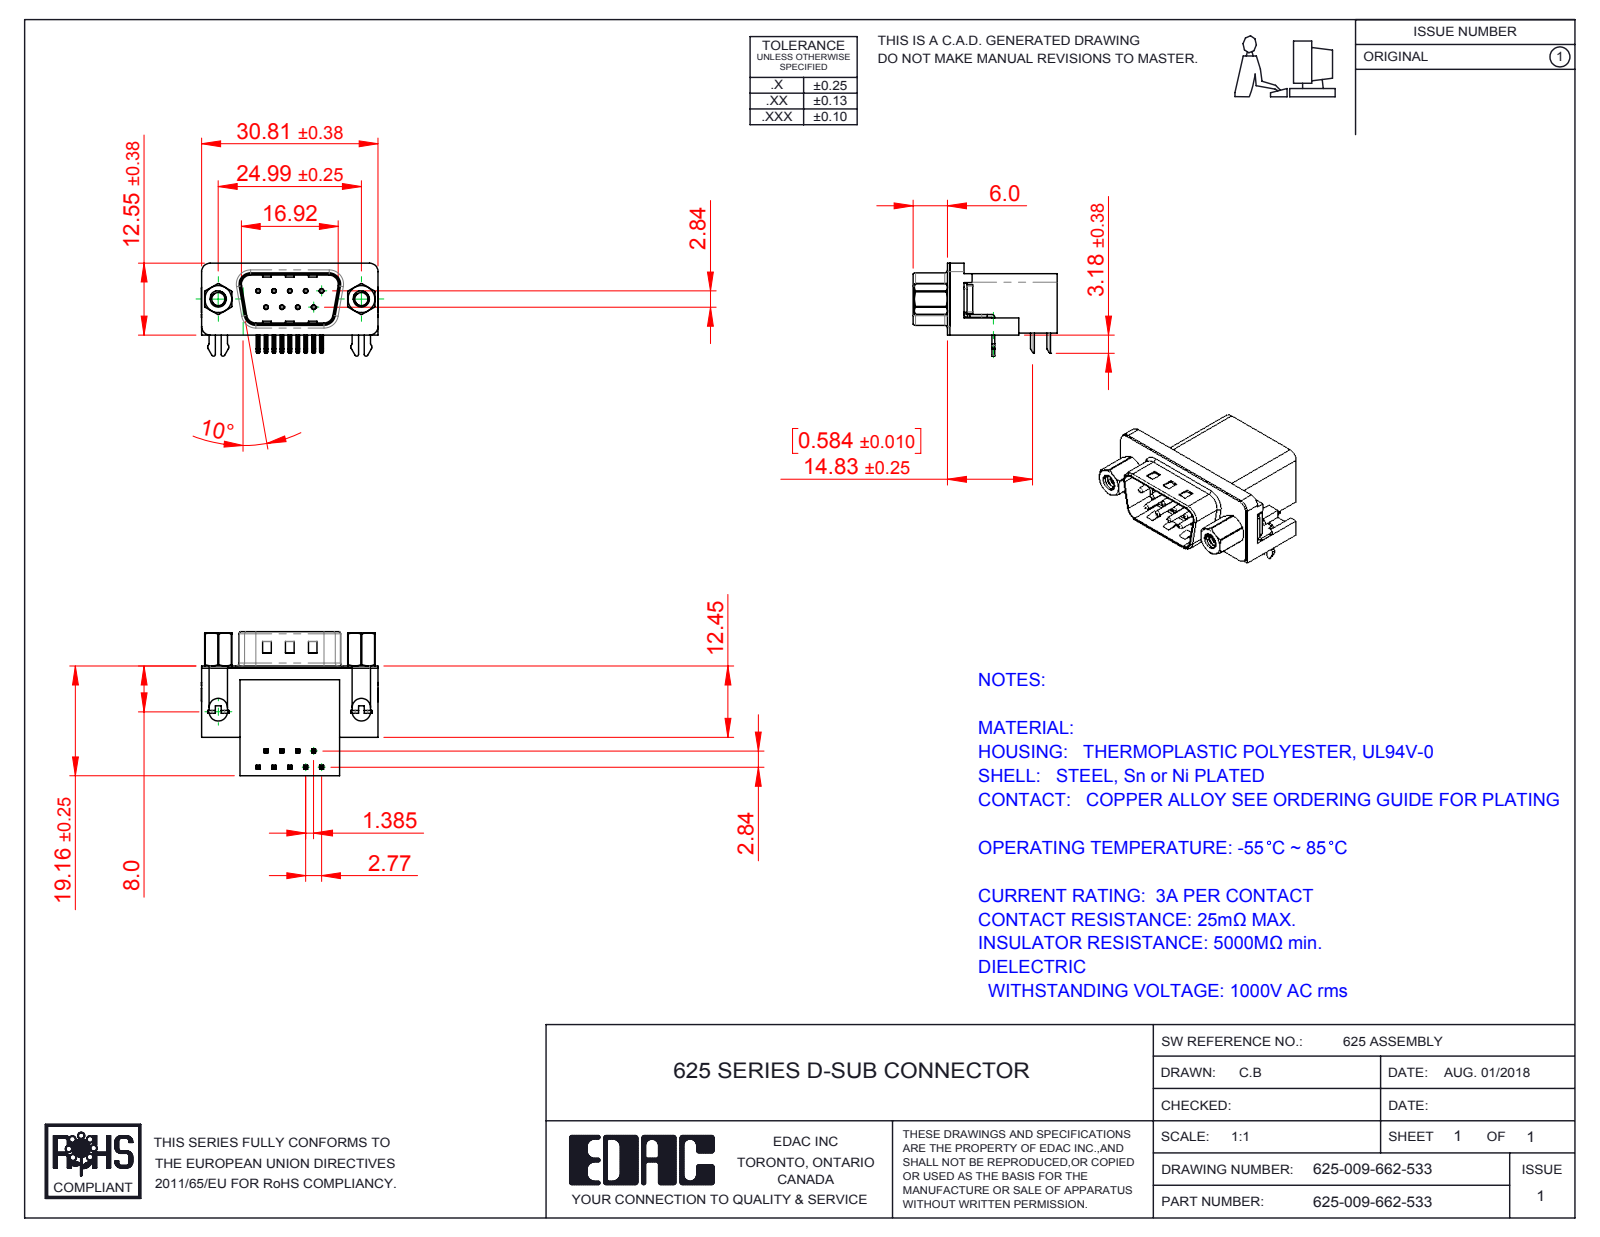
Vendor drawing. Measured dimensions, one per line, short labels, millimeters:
name: 625 Shell_9 Socket; 625 2 Prong Board Lock; 625 Housing_9 Socket; 625 4-40 Hex Standoff 5 (+4 more)
written by: SolidWorks 2016 (CONFIG_CONTROL_DESIGN)
unit: mm
bodies: 17 solids, 1159 faces (627 planar, 397 cylindrical, 135 other)
size: 30.89 × 25.16 × 16.25
volume: 4 688 mm³; area: 5 440 mm²
holes: 9× ⌀0.35, 9× ⌀0.8, 2× ⌀2.26, 2× ⌀2.29, 2× ⌀4, 2× ⌀4.8, 2× ⌀5
bosses: 9× ⌀0.75, 2× ⌀4.9, 2× ⌀4.75, 2× ⌀3.9, 2× ⌀2.79
rounds: 44× R0.25, 18× R0.12, 16× R1, 14× R0.5, 8× R1.5, 8× R1.6, 4× R0.32, 4× R0.9
face distances: 0.4, 10.34, 18.76, 19.16, 16.26, 2.5, 2.9, 0.35, 10.69, 0.5
hole spacings: 3.16, 2.77, 5.54, 5.03, 5.04, 8.31, 7.48, 7.49
